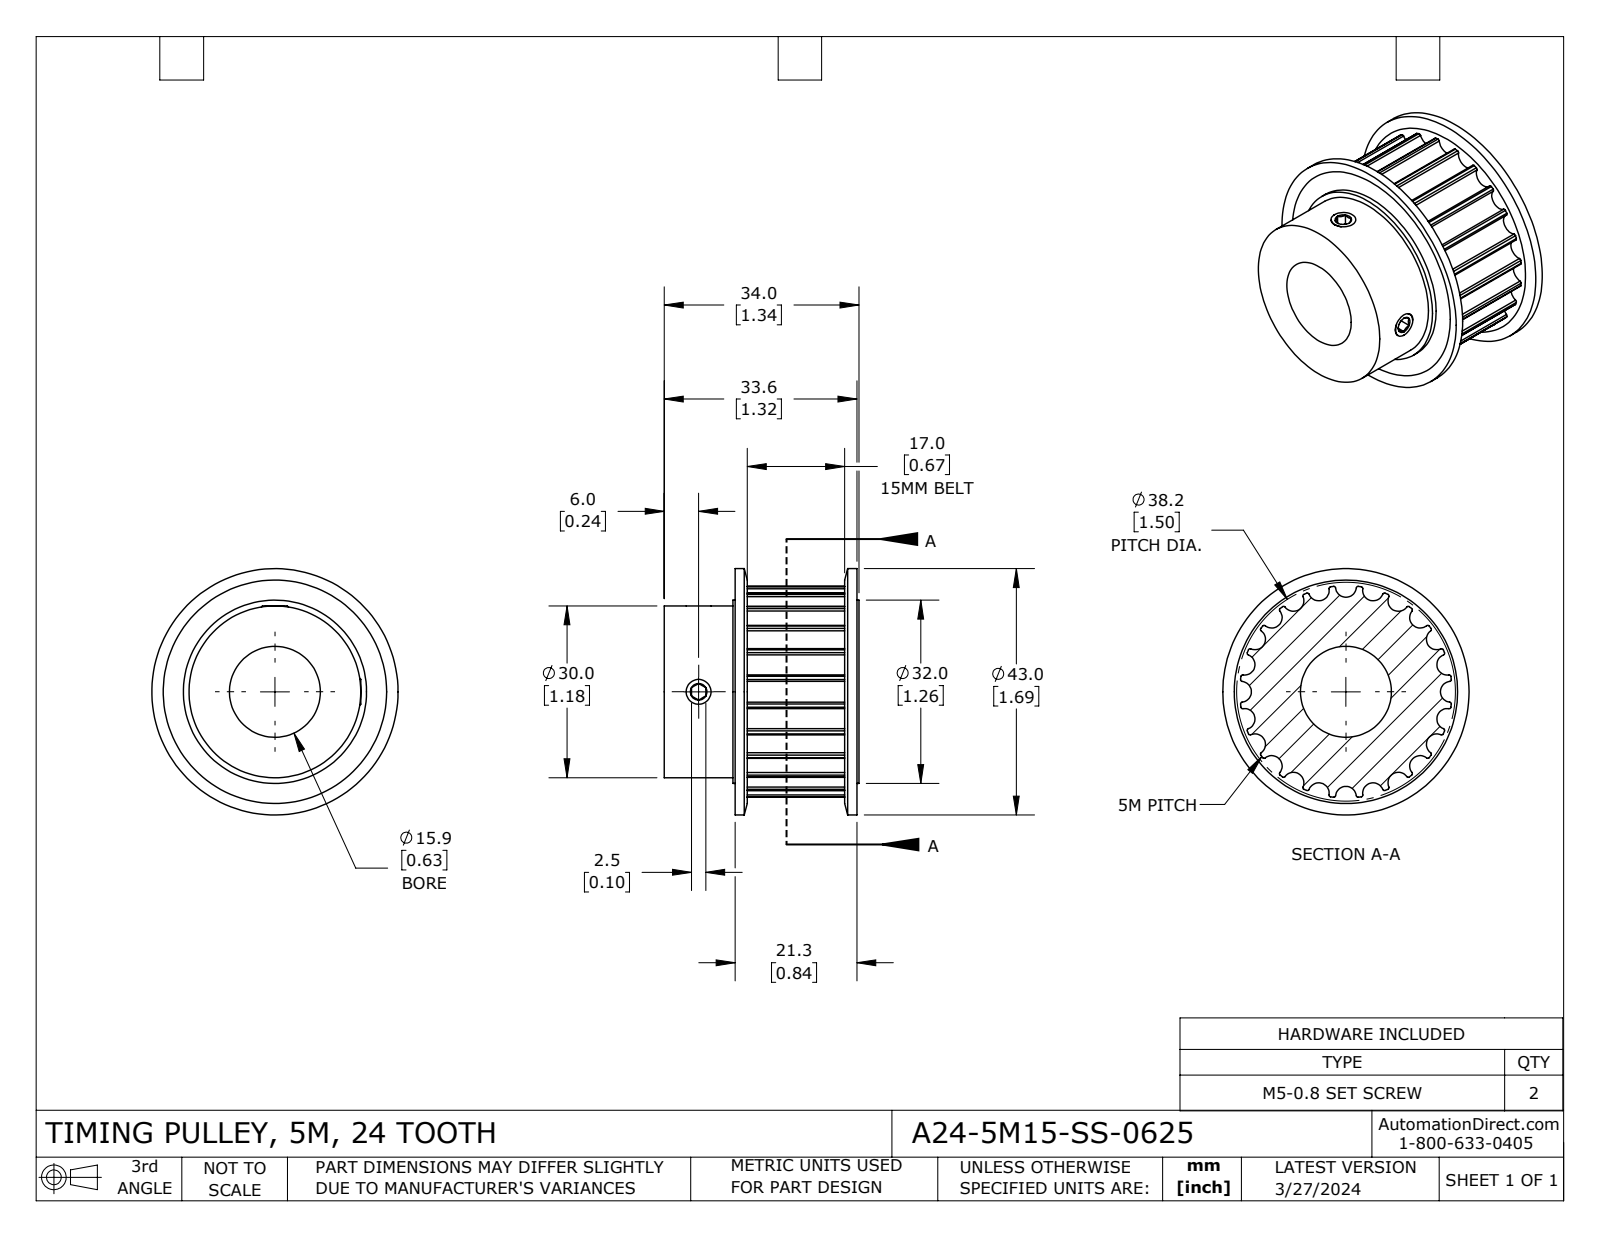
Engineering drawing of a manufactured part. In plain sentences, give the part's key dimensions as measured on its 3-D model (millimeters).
The part is named "A24-5M15-SS-0625". Its 3-D file was written by "SolidWorks 2021 (CONFIG_CONTROL_DESIGN)". It is 5 solids with 202 faces: 25 planar, 143 cylindrical and 34 other. Overall it measures 43 by 43 by 34 millimeters. Its volume is 23 709 cubic millimeters and its surface area 11 330 square millimeters. Round holes: 2 of diameter 4.2, 1 of diameter 15.88, 1 of diameter 32. Round bosses or shafts: 2 of diameter 5, 1 of diameter 43, 1 of diameter 30. Partial cylindrical surfaces (rounded edges, fillets, slot ends): 48 of radius 0.3, 24 of radius 1.82, 1 of radius 18.52. The main face-to-face distances are 1.6, 18.6, 2.5, 19.5, 17, 34, 31.5, 14.5, 0.9, 21.1.
